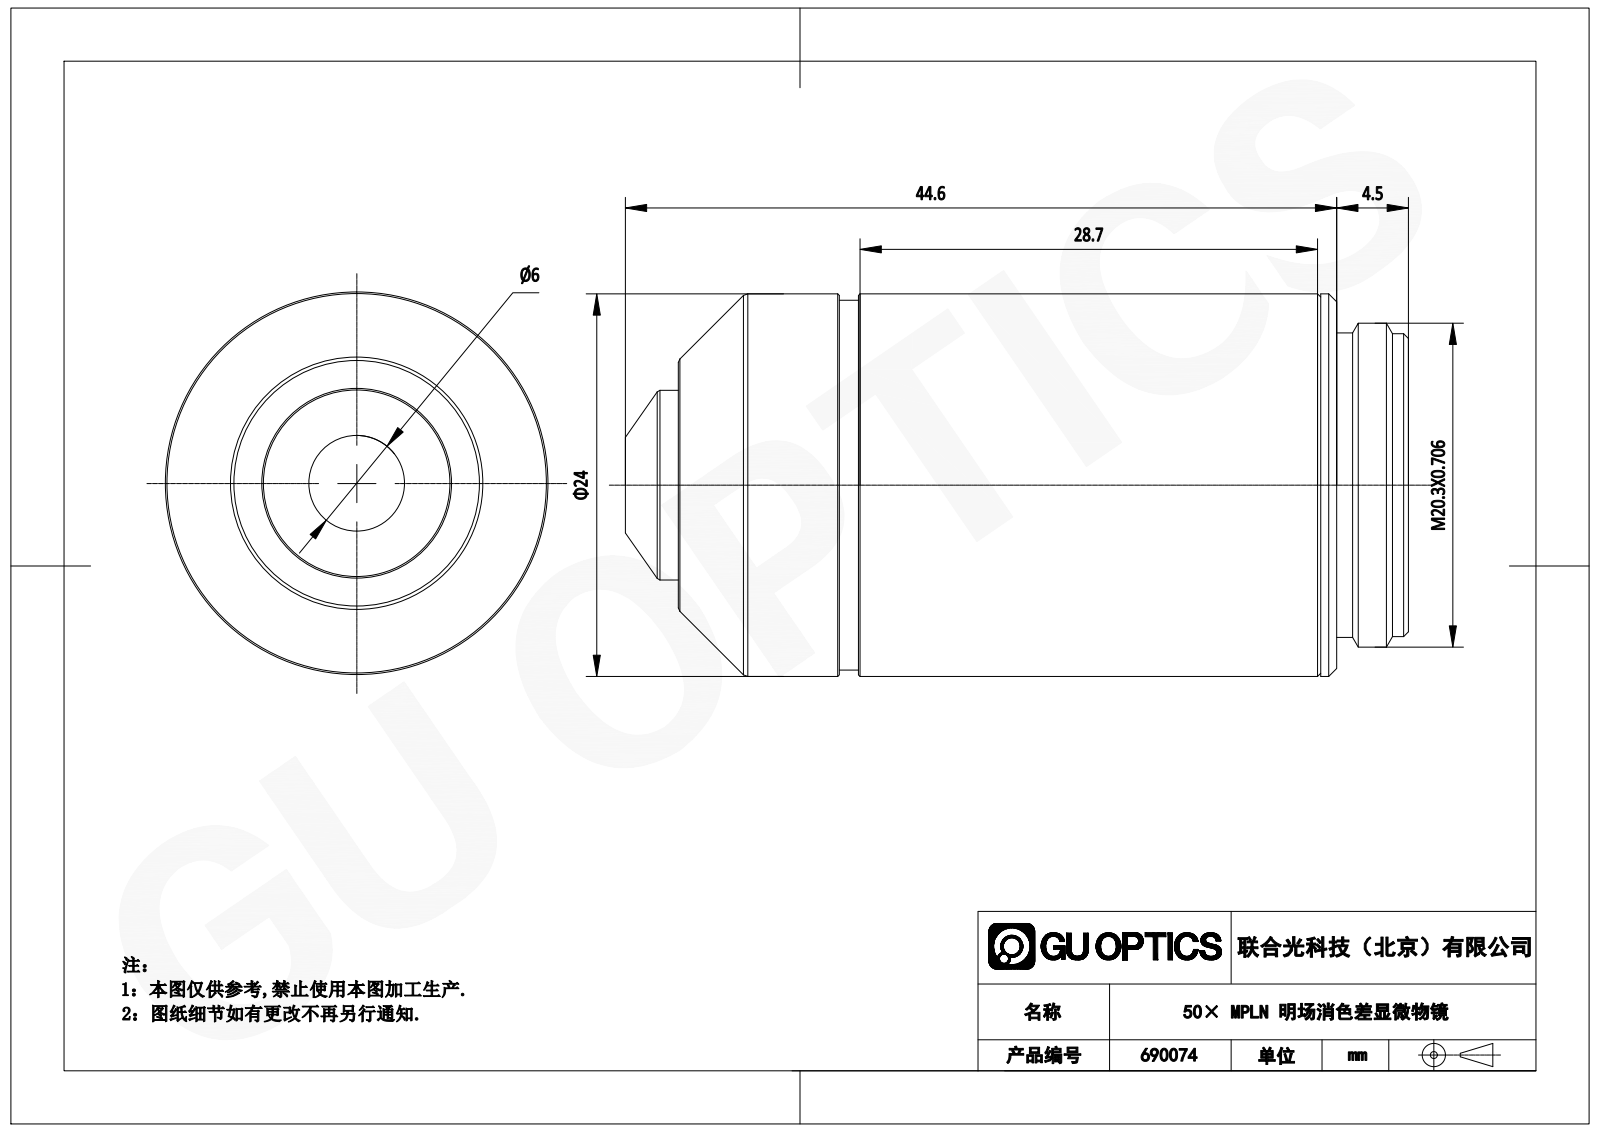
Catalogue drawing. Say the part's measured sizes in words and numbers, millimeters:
The part is named "690074". Its 3-D file was written by "SolidWorks 2020 (CONFIG_CONTROL_DESIGN)". It is 1 solid with 47 faces: 7 planar, 16 cylindrical and 24 other. Overall it measures 49.12 by 24 by 24 millimeters. Its volume is 19 689 cubic millimeters and its surface area 4 228 square millimeters. Round bosses or shafts: 1 of diameter 24, 1 of diameter 23.2, 1 of diameter 20.32, 1 of diameter 19.1, 1 of diameter 19, 1 of diameter 11.9. The main face-to-face distances are 4.5, 41.3, 45.8, 3.32, 44.62, 49.12, 13.42, 14.62, 10.1, 11.3.
